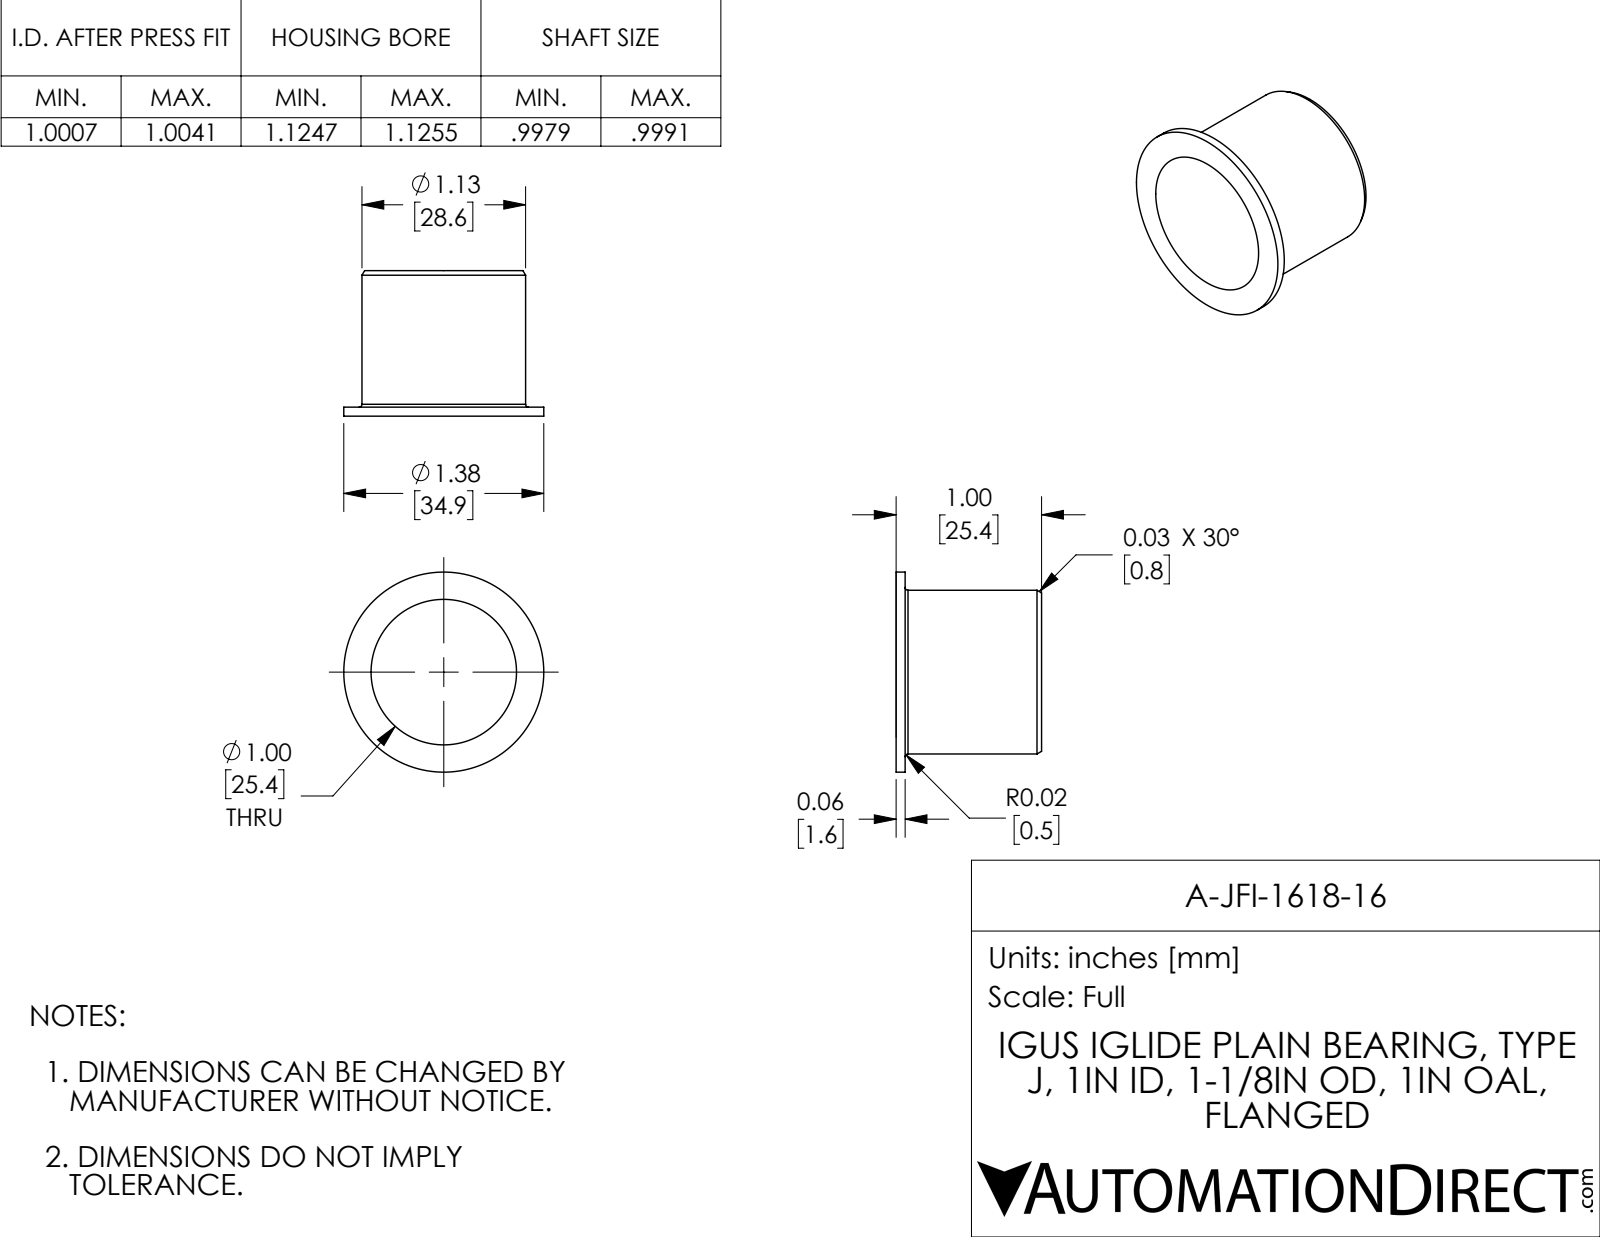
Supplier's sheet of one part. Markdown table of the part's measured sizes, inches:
| quantity | value |
| --- | --- |
| part name | A-JFI-1618-16 |
| STEP written by | SolidWorks 2017 (AUTOMOTIVE_DESIGN) |
| units | inches |
| bodies | 1 solid, 13 faces (3 planar, 6 cylindrical, 4 other) |
| overall size | 1.375 × 1.375 × 1 |
| volume | 0.238 in³ |
| surface area | 8.047 in² |
| round holes (diameter × count) | 1 × 1 |
| round bosses / shafts (diameter × count) | 1.375 × 1, 1.125 × 1 |
| main face-to-face distances | 0.062, 1, 0.938 |
